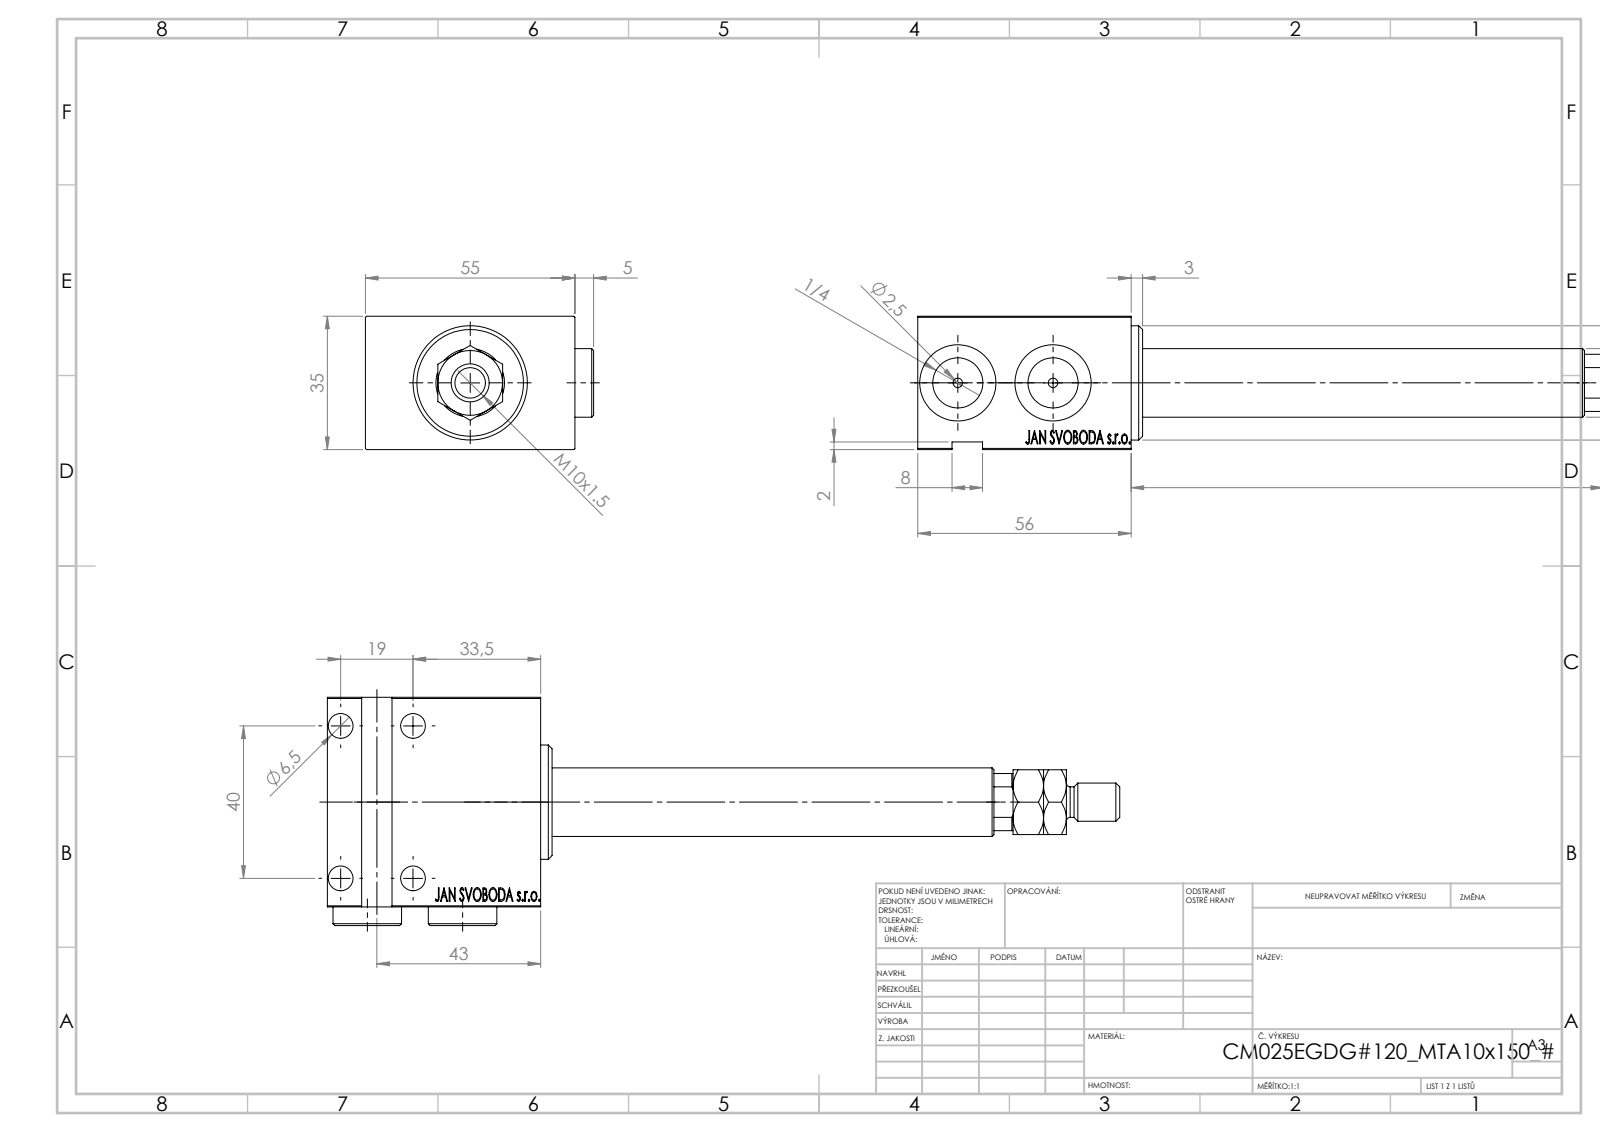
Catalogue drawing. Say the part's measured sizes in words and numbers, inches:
The part is named "V450CM_E_VCP; V450CM_E_Body; MTA; Zatka_OIL_PORT (+1 more)". Its 3-D file was written by "SolidWorks 2019 (CONFIG_CONTROL_DESIGN)". It is 6 solids with 952 faces: 456 planar, 68 cylindrical and 428 other. Overall it measures 8.189 by 2.358 by 1.378 inches. Its volume is 8.102 cubic inches and its surface area 64.89 square inches. Round holes: 4 of diameter 0.256, 2 of diameter 0.098, 2 of diameter 0.413, 2 of diameter 0.518, 2 of diameter 0.787, 1 of diameter 0.335, 1 of diameter 0.709, 1 of diameter 0.984. Round bosses or shafts: 2 of diameter 0.709, 1 of diameter 1.181, 1 of diameter 1.063, 1 of diameter 0.394, 1 of diameter 0.315. Partial cylindrical surfaces (rounded edges, fillets, slot ends): 2 of radius 0.207, 1 of radius 0.335. The main face-to-face distances are 1.378, 2.205, 0.197, 2.165, 2.161, 2.008, 1.299, 0.079, 0.669, 0.118. The hole center spacings are 0.748, 1.575, 1.743, 0.984.
